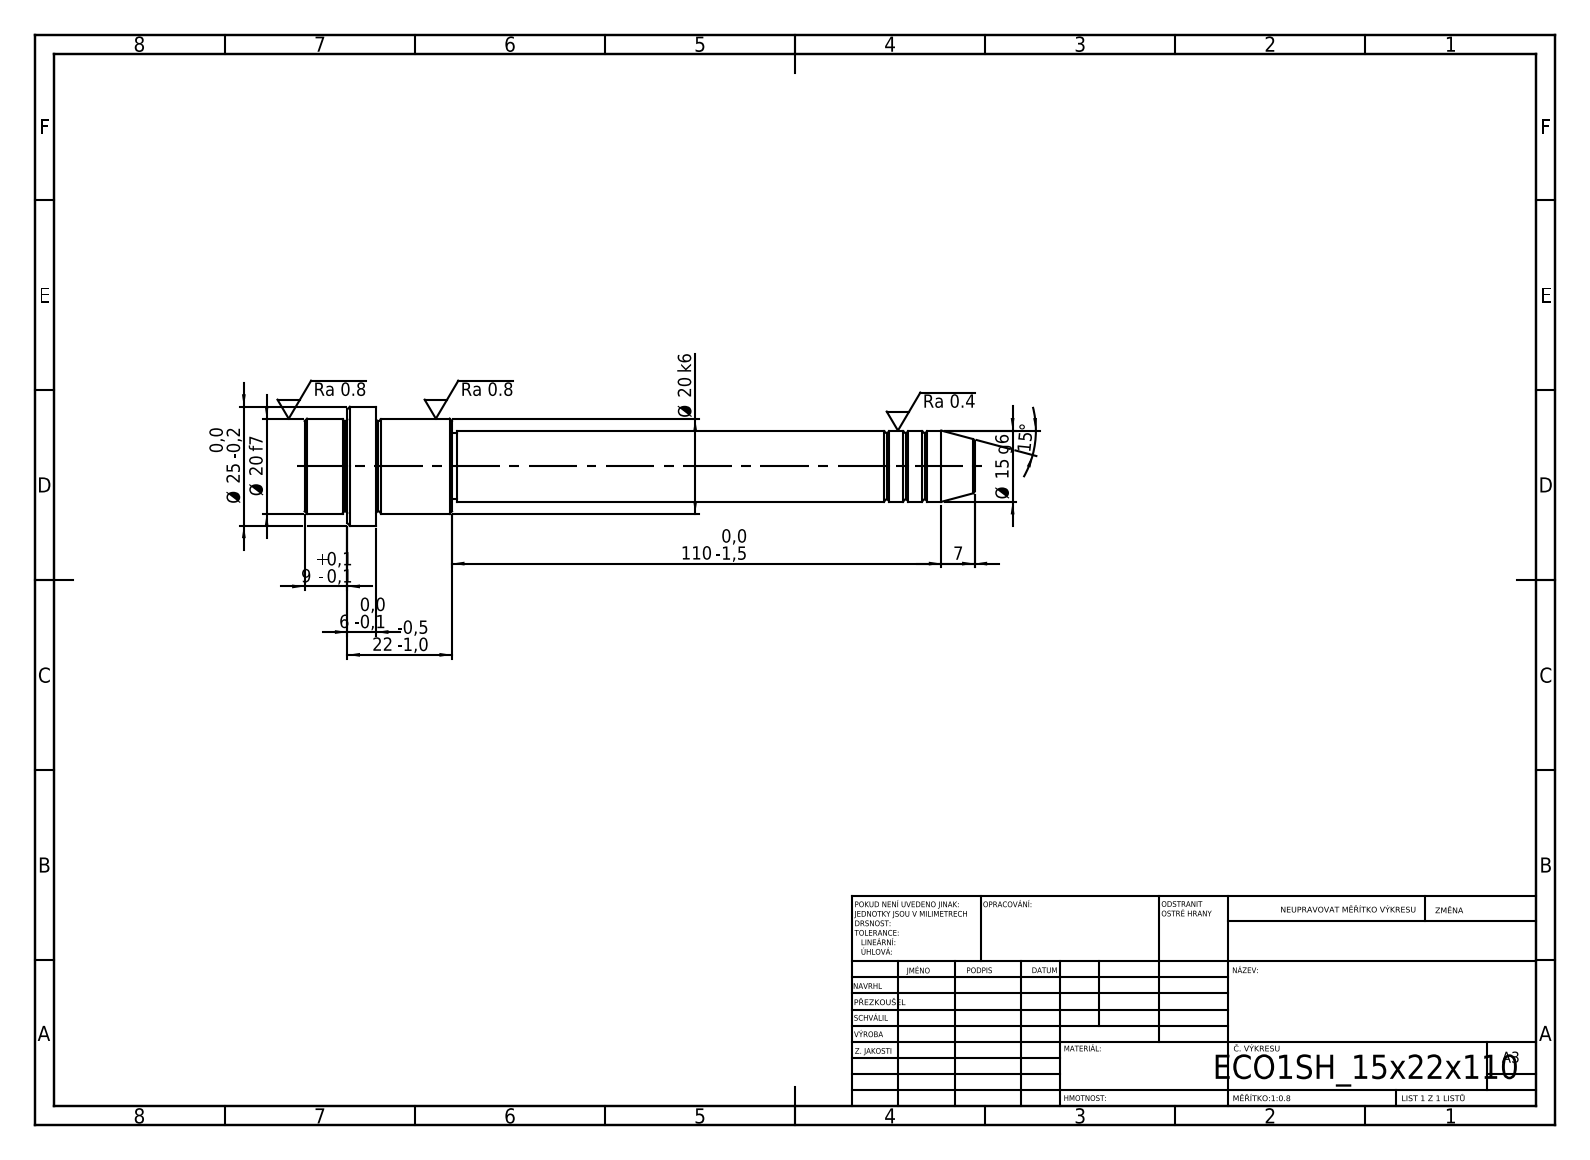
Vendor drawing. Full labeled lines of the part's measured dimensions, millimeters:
STEP written by: SolidWorks 2019 (CONFIG_CONTROL_DESIGN)
Units: millimetres
Bodies: 1 solid, 52 faces (6 planar, 16 cylindrical, 30 other)
Overall size (bounding box): 141 × 25 × 25
Volume: 29 803 mm³ · Surface area: 8 213 mm²
Round bosses / shafts (diameter × count): ⌀25 ×1, ⌀20 ×1, ⌀15 ×1, ⌀14 ×1
Main face-to-face distances: 15, 6, 9, 16, 22, 31, 110, 126, 132, 141
